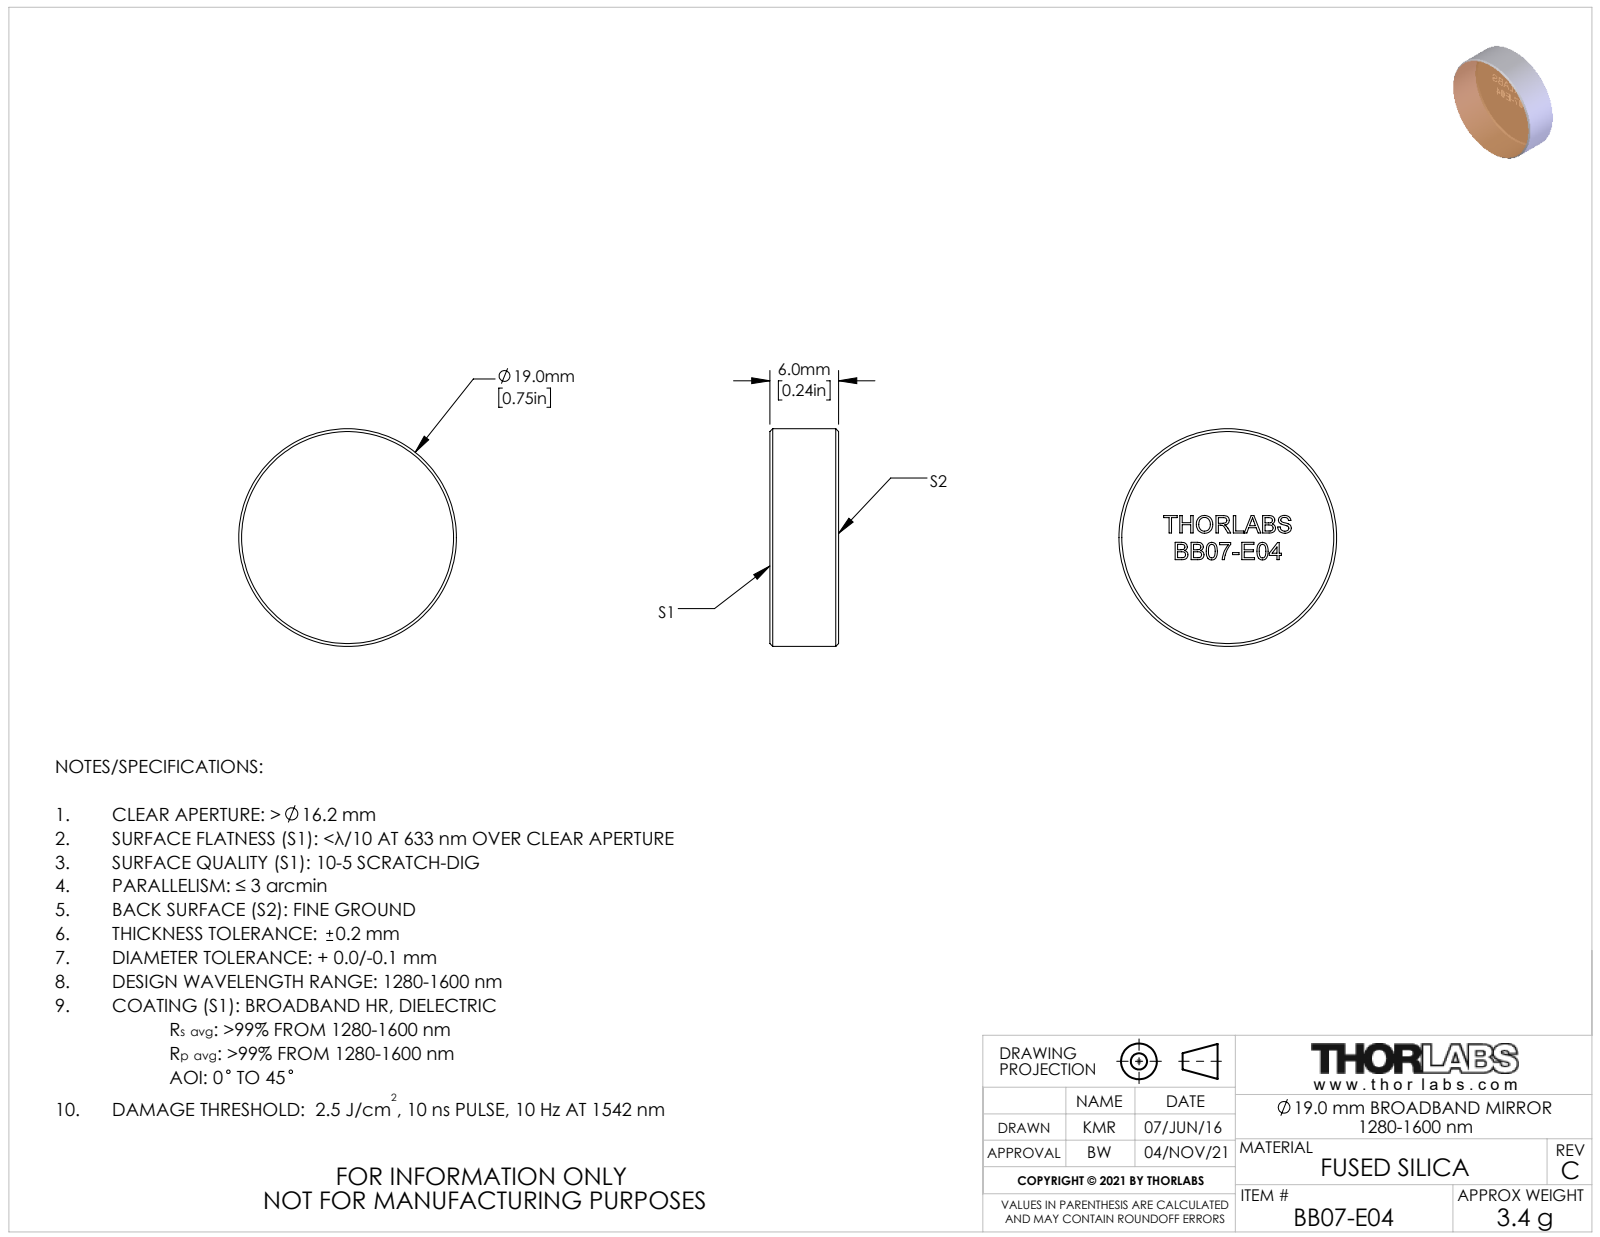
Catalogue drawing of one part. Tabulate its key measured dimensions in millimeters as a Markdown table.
| quantity | value |
| --- | --- |
| part name | TTN024108-E0W |
| STEP written by | SolidWorks 2016 (CONFIG_CONTROL_DESIGN) |
| units | millimeters |
| bodies | 1 solid, 233 faces (142 planar, 2 cylindrical, 89 other) |
| overall size | 19 × 19 × 6 |
| volume | 1 697 mm³ |
| surface area | 908 mm² |
| round bosses / shafts (diameter × count) | 19 × 1 |
| main face-to-face distances | 6, 1.52, 2.33, 1.34, 2.16, 0.93, 1.17, 2.35, 4.08, 0.74 |
